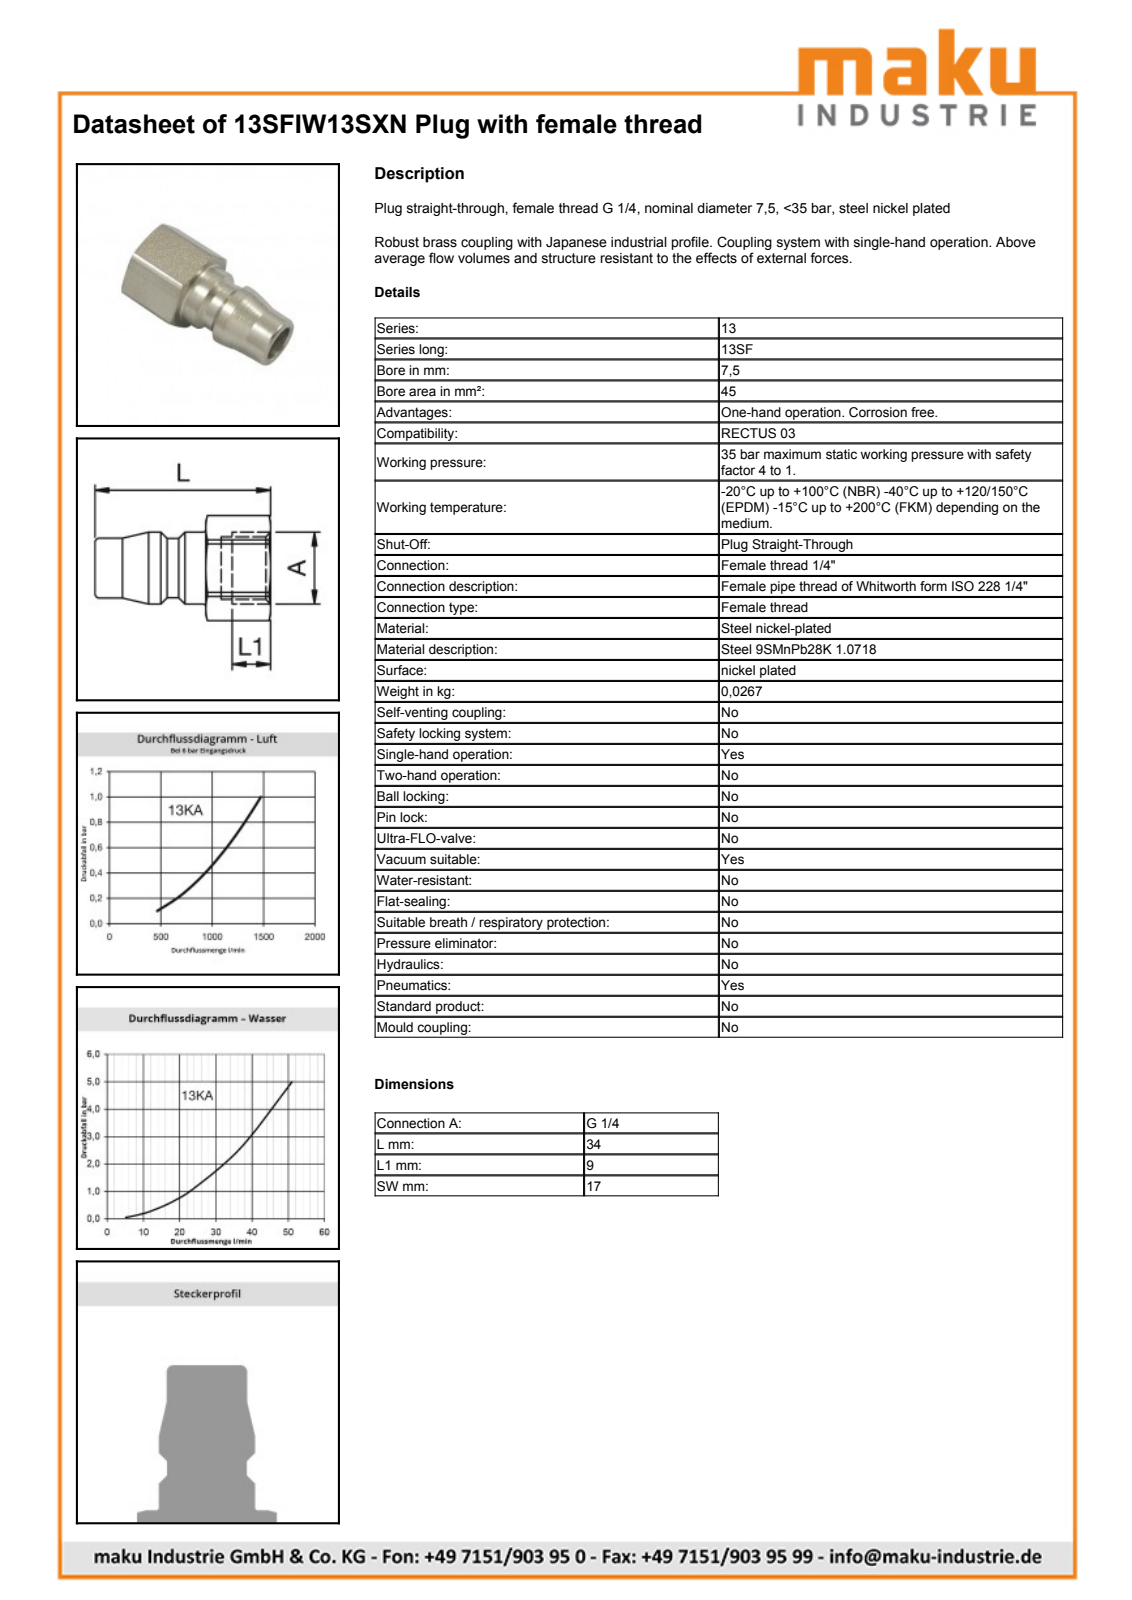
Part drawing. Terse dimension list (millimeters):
name: D112254
written by: Autodesk Inventor 2013 (AUTOMOTIVE_DESIGN)
unit: mm
bodies: 1 solid, 40 faces (10 planar, 12 cylindrical, 18 other)
size: 34 × 19.15 × 17
volume: 3 479 mm³; area: 2 878 mm²
holes: 1× ⌀7.5, 1× ⌀11.8
bosses: 1× ⌀13.1, 1× ⌀10.9, 1× ⌀10.8
rounds: 1× R9.57
face distances: 17, 13.8, 2.8, 11, 20.2, 23, 34
